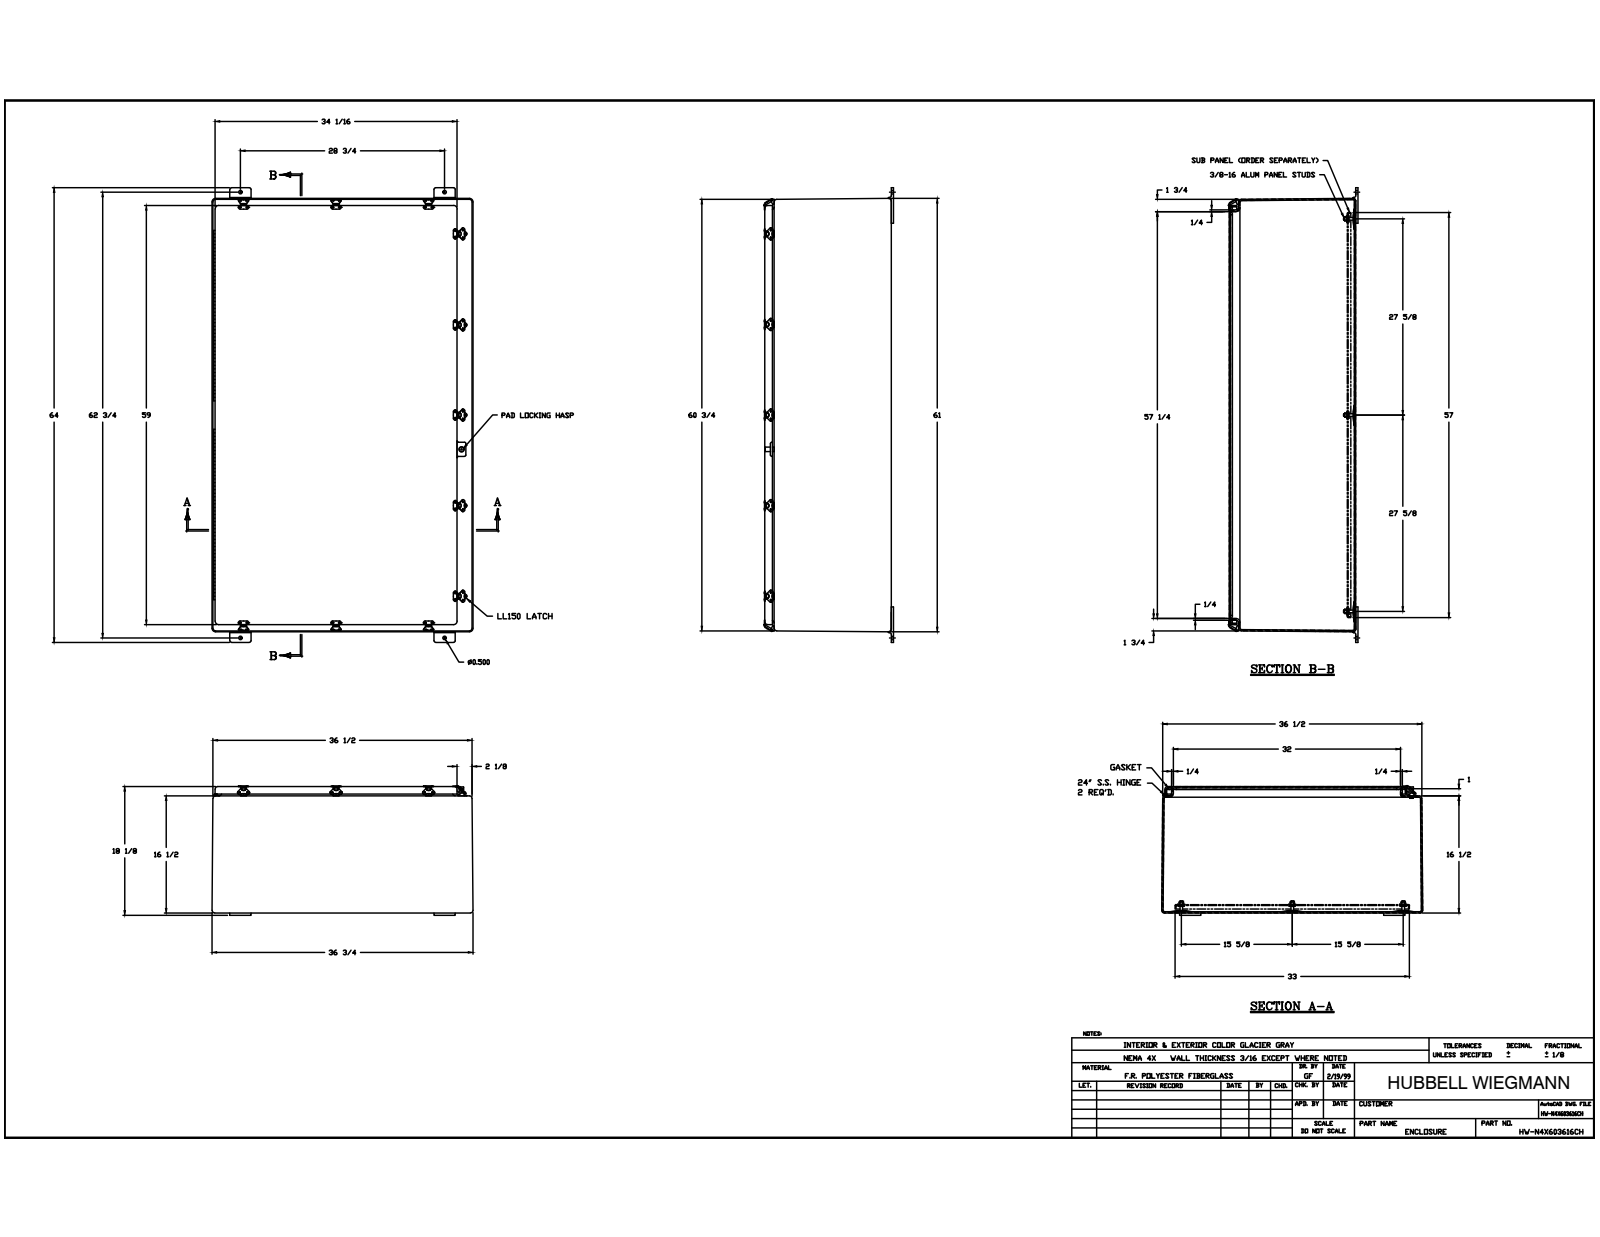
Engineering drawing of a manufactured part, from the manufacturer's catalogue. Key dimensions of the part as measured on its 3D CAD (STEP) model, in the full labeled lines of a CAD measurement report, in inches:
Part name (STEP PRODUCT): WPN603616SHWT; WPN603616HWTPCVR; N603616G; WP6036WU (+8 more)
STEP written by: Autodesk Inventor 2014 (AUTOMOTIVE_DESIGN)
Units: inches
Bodies: 127 solids, 3132 faces (1212 planar, 1300 cylindrical, 620 other)
Overall size (bounding box): 64 × 36.75 × 18.366
Volume: 1 454 in³ · Surface area: 17 030 in²
Round holes (diameter × count): ⌀0.13 ×72, ⌀0.063 ×44, ⌀0.138 ×22, ⌀0.187 ×22, ⌀0.065 ×16, ⌀0.375 ×8, ⌀0.5 ×4, ⌀0.135 ×3, ⌀0.156 ×3, ⌀0.125 ×1, ⌀0.201 ×1, ⌀0.25 ×1
Round bosses / shafts (diameter × count): ⌀0.14 ×44, ⌀0.297 ×16, ⌀0.5 ×11, ⌀0.2 ×3, ⌀0.25 ×1, ⌀0.201 ×1
Partial cylindrical surfaces — rounded edges, fillets, slot ends (radius × count): R0.01 ×243, R0.03 ×44, R0.313 ×41, R0.375 ×23, R0.21 ×22, R1.186 ×22, R0.25 ×18, R0.037 ×14
Main face-to-face distances: 0.187, 0.125, 17.813, 17.687, 0.188, 17.624, 17.499, 36.562, 60.813, 36.75
Hole centre spacings: 7.5, 15.5, 28, 12.75, 1, 8, 12.5, 13.031
